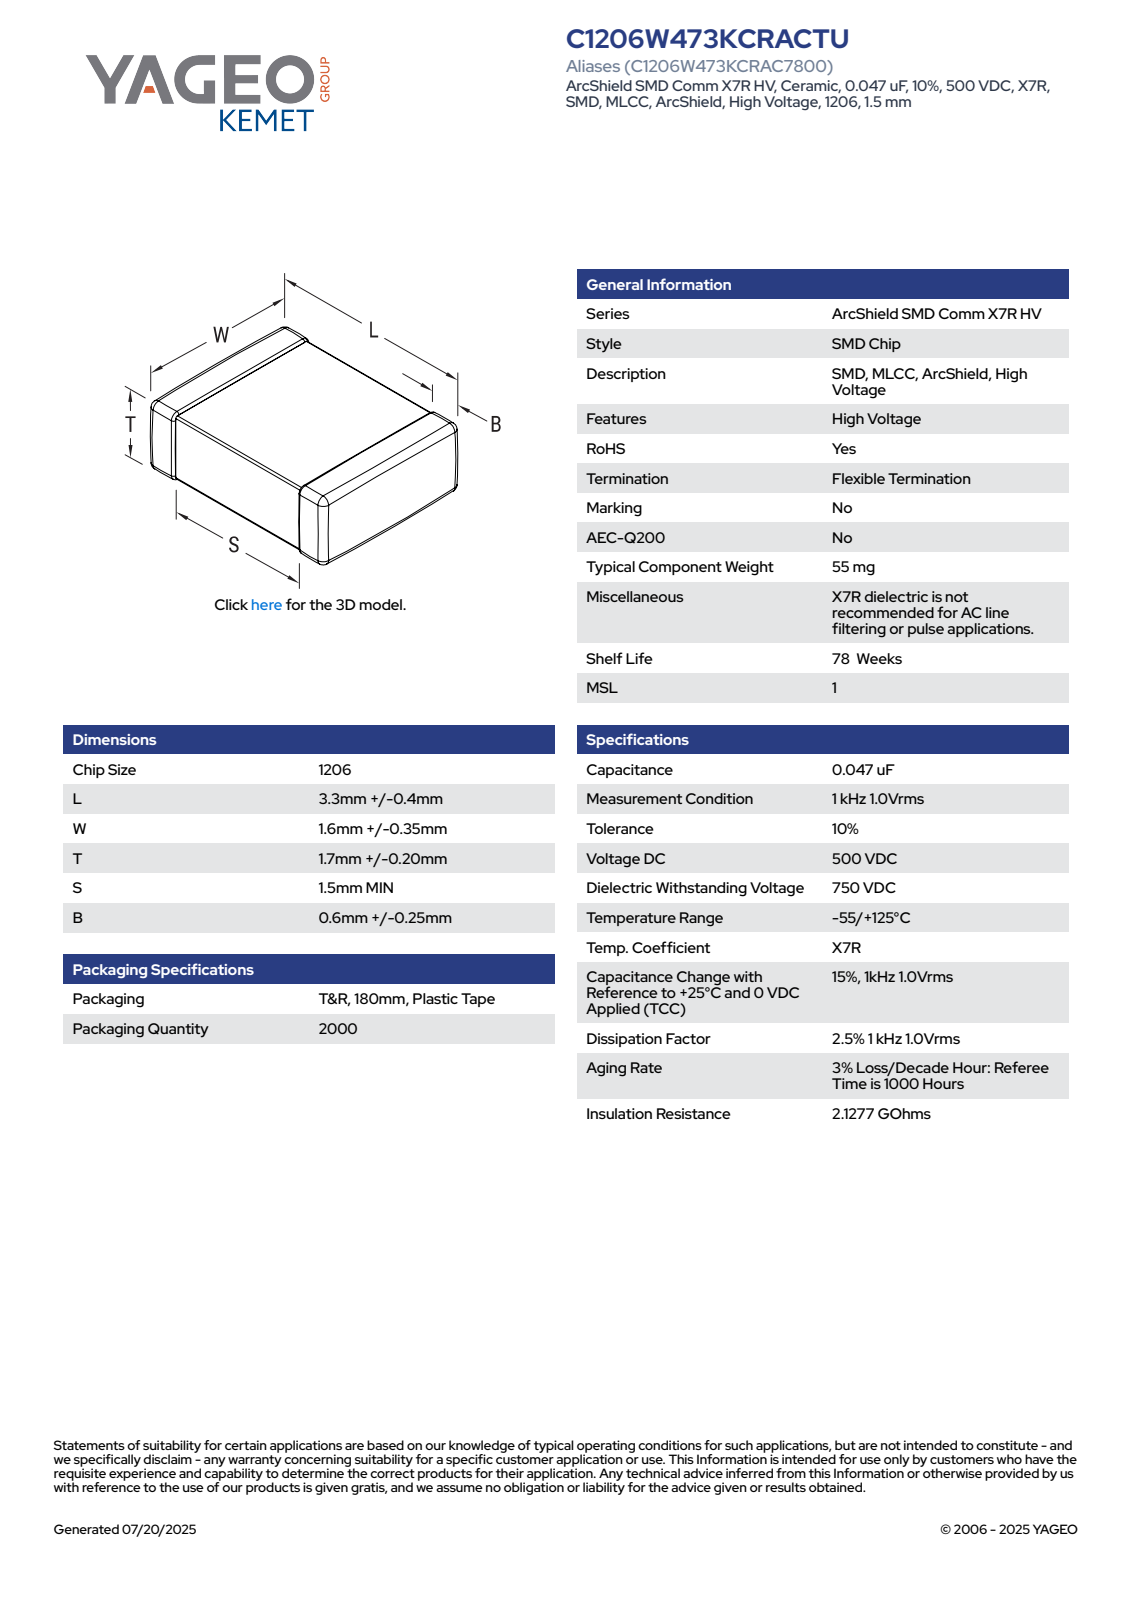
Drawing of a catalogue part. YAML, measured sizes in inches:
part_name: "CCS_CCSTD_1206_L3.7W1.95T1.9B0.6"
step_written_by: "SolidWorks 2021 (AUTOMOTIVE_DESIGN)"
units: inches
bodies: {solids: 4, faces: 129, planar: 71, cylindrical: 42, other: 16}
overall_size: [0.146, 0.077, 0.075]
volume: 0.001
surface_area: 0.056
face_to_face_distances: [0.073, 0.075, 0.072, 0.074, 0.146, 0.075, 0.077, 0.067, 0.078, 0.079]
